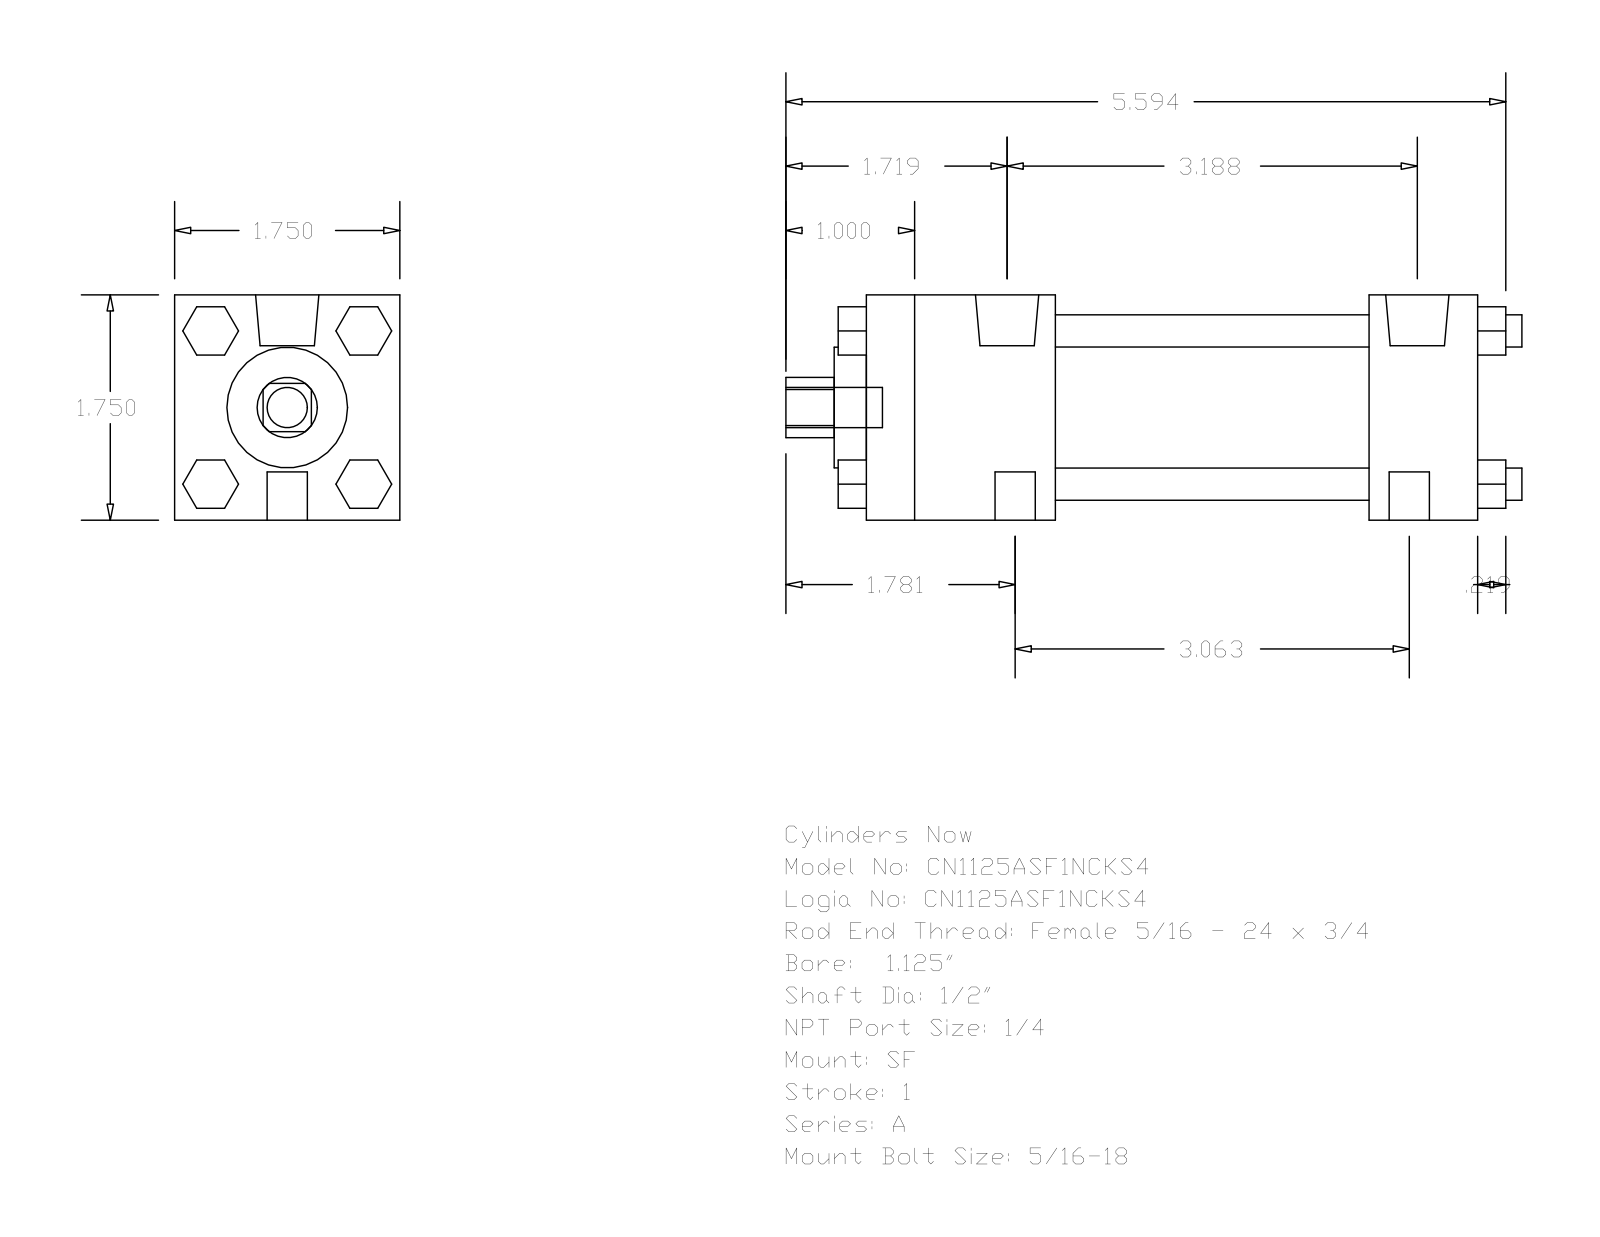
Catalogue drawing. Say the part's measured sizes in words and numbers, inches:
The part is named "A_SF__0112_0.5". Its 3-D file was written by "GSSL Pune (CONFIG_CONTROL_DESIGN)". It is 0 solids with 120 faces: 92 planar, 28 cylindrical and 0 other. Overall it measures 5.719 by 1.75 by 1.75 inches. Round holes: 1 of diameter 0.5, 1 of diameter 0.937, 1 of diameter 1.255. Round bosses or shafts: 4 of diameter 0.25, 3 of diameter 0.313, 2 of diameter 0.492, 2 of diameter 0.219. Partial cylindrical surfaces (rounded edges, fillets, slot ends): 1 of radius 0.234. The main face-to-face distances are 1.75, 4.75, 3.906, 0.844, 1.469, 2.437, 3.281, 0.375, 0.22, 0.375.
